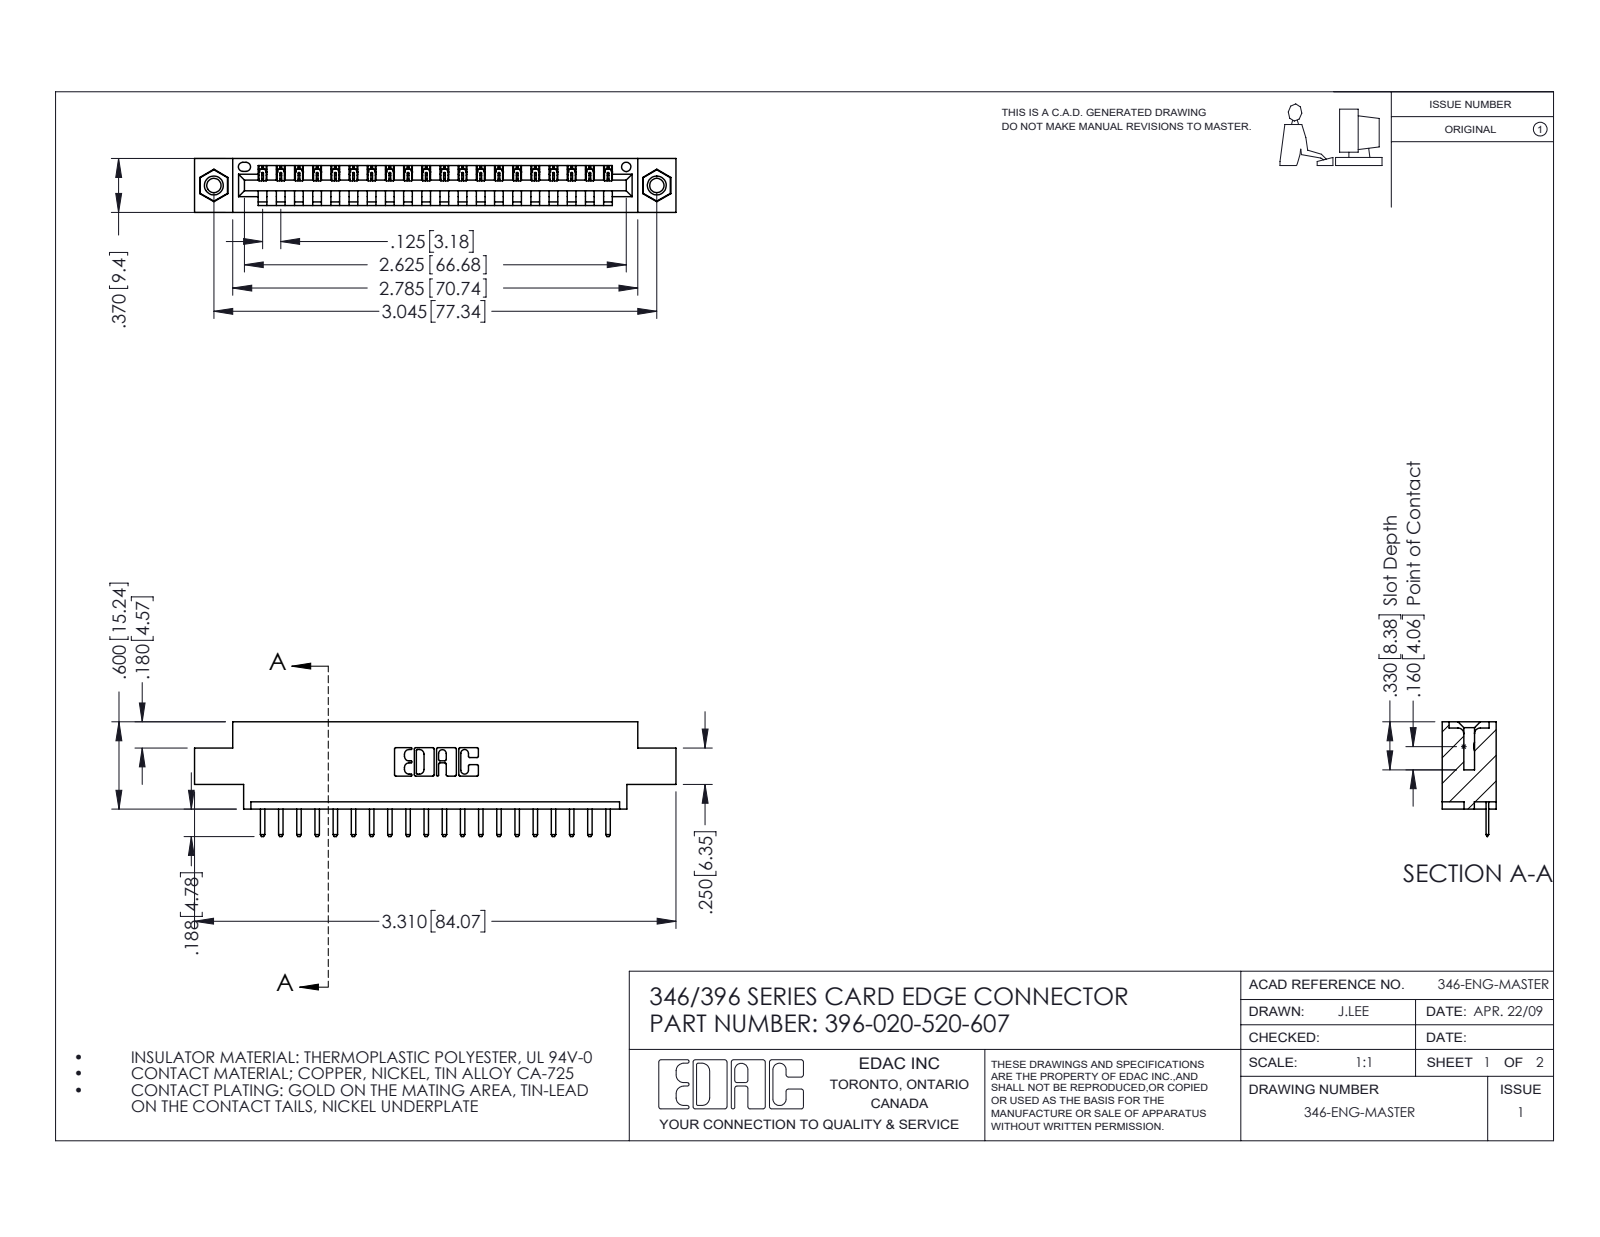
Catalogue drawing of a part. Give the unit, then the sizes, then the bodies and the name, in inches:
Units: inches
Overall size (bounding box): 3.31 × 0.788 × 0.37
Round holes (diameter × count): ⌀0.098 ×2, ⌀0.125 ×2, ⌀0.156 ×2, ⌀0.064 ×1
Round bosses / shafts (diameter × count): ⌀0.155 ×2
Partial cylindrical surfaces — rounded edges, fillets, slot ends (radius × count): R0.01 ×42, R0.006 ×40, R0.01 ×22, R0.007 ×6, R0.031 ×6, R0.026 ×3, R0.031 ×2, R0.04 ×2
Main face-to-face distances: 0.37, 0.048, 0.322, 0.25, 0.222, 0.148, 0.1, 0.174, 0.072, 0.298
Hole centre spacings: 0.246, 2.837, 3.045
Volume: 0.468 in³ · Surface area: 14.5 in²
Bodies: 23 solids, 1426 faces (952 planar, 458 cylindrical, 16 other)
Part name (STEP PRODUCT): 345-250-001_345-250-005-103; 346 Part_0.170 Offset - 0.156 Dia-TI; 345-292-001_345-293-120; 396-020-520-607
STEP written by: SolidWorks 2016 (CONFIG_CONTROL_DESIGN)
